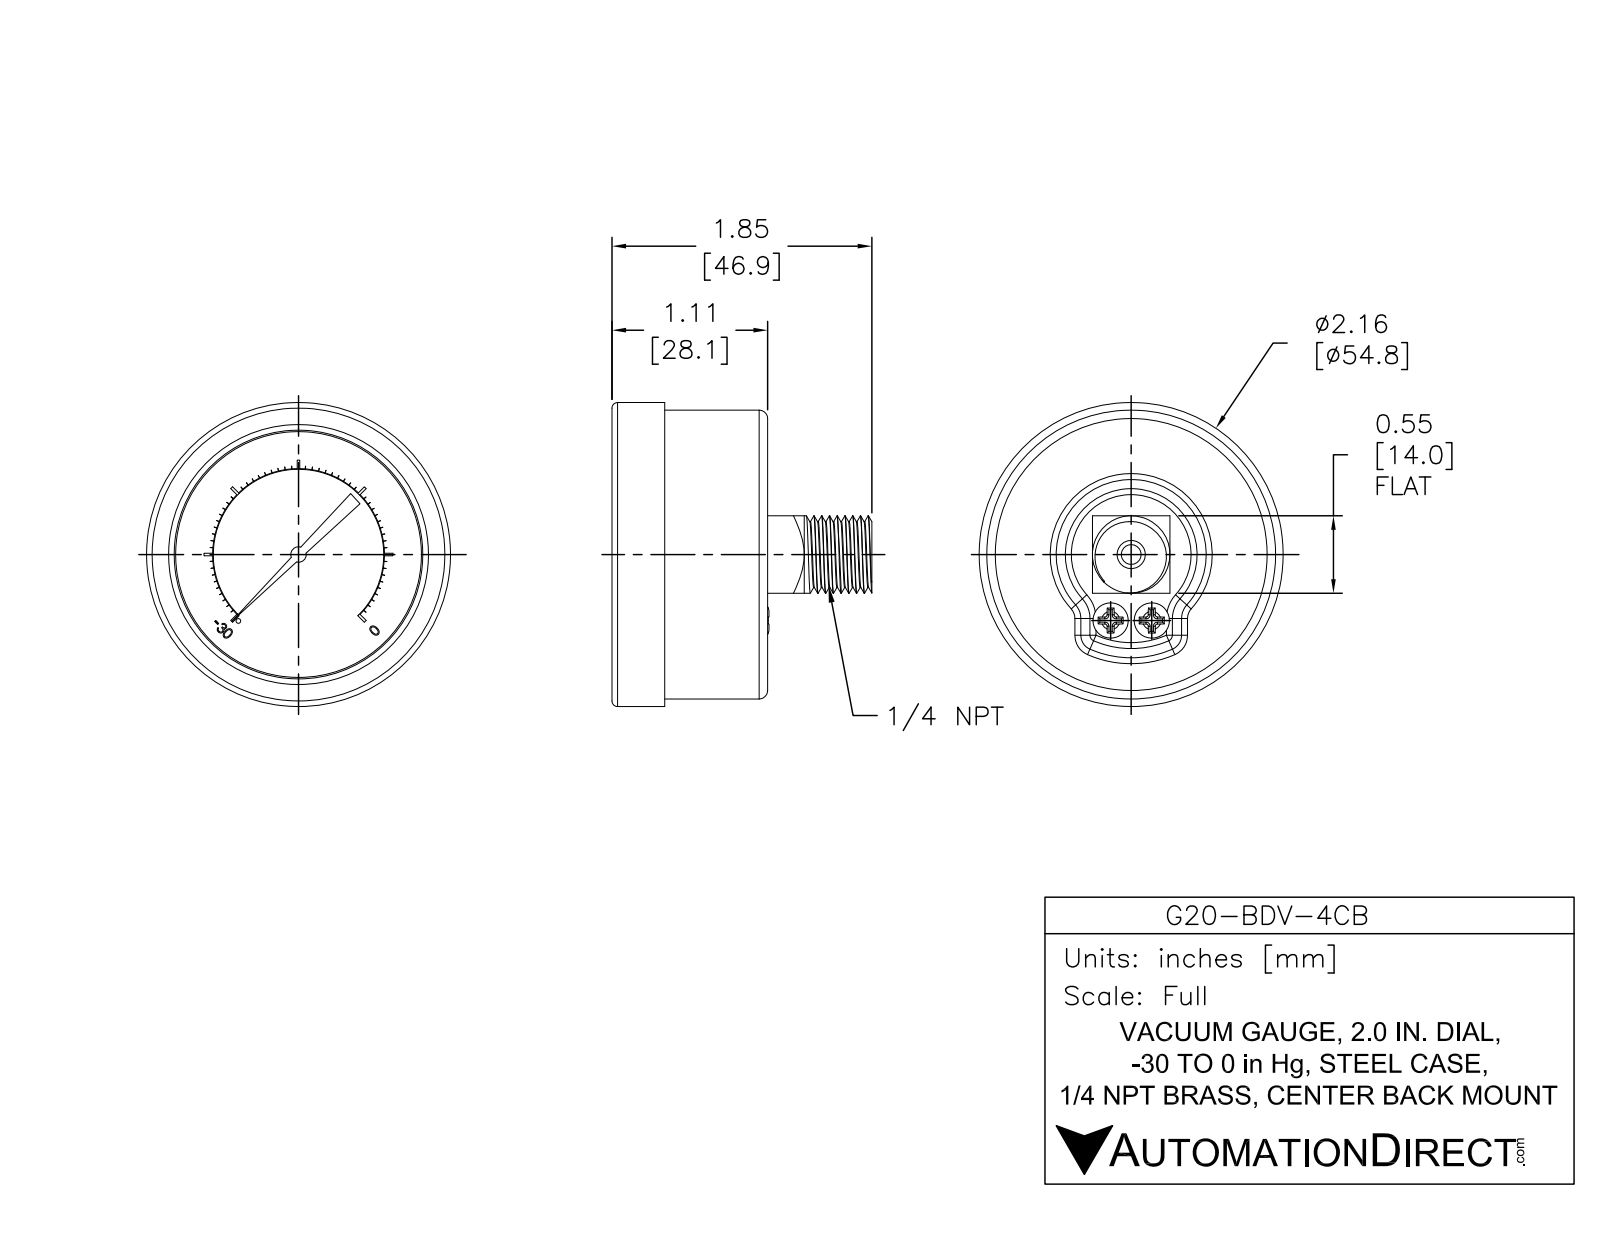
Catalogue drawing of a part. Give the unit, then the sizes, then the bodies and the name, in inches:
Units: inches
Overall size (bounding box): 2.158 × 2.158 × 1.845
Round holes (diameter × count): ⌀0.14 ×1, ⌀1.745 ×1
Round bosses / shafts (diameter × count): ⌀0.25 ×2, ⌀2.158 ×1, ⌀2.05 ×1, ⌀0.55 ×1, ⌀0.11 ×1, ⌀0.102 ×1, ⌀0.055 ×1
Partial cylindrical surfaces — rounded edges, fillets, slot ends (radius × count): R0.06 ×4, R0.605 ×1, R0.61 ×1
Main face-to-face distances: 0.815, 1.105, 0.29, 0.73, 0.085, 0.375, 0.1, 1.005, 0.63, 0.715
Volume: 3.201 in³ · Surface area: 18.16 in²
Bodies: 1 solid, 379 faces (240 planar, 70 cylindrical, 69 other)
Part name (STEP PRODUCT): G20-BDV-4CB
STEP written by: SolidWorks 2021 (AUTOMOTIVE_DESIGN)
